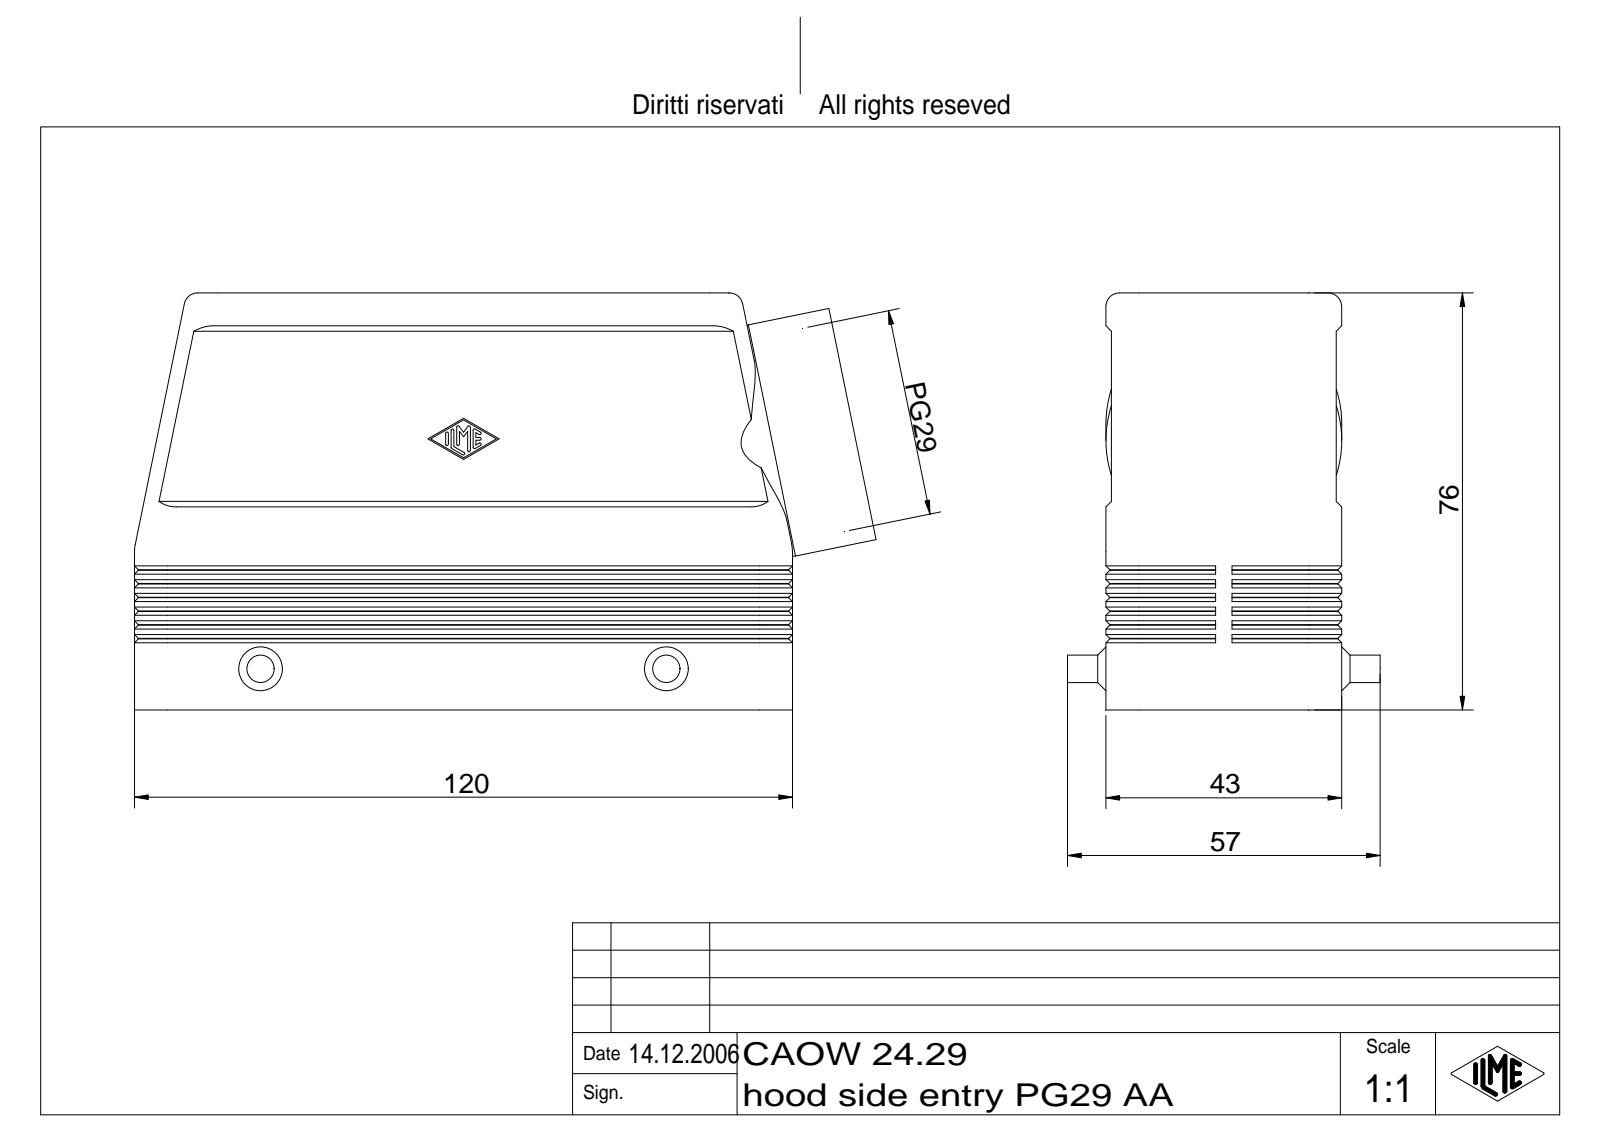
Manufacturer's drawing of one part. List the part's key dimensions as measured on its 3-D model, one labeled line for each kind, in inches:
Part name (STEP PRODUCT): CAO Tüllengehäuse 2 Bügel für einen Einsatz
STEP written by: Autodesk Inventor 7 (AUTOMOTIVE_DESIGN)
Units: inches
Bodies: 1 solid, 526 faces (192 planar, 134 cylindrical, 200 other)
Overall size (bounding box): 5.324 × 2.992 × 2.244
Volume: 5.373 in³ · Surface area: 89.25 in²
Round holes (diameter × count): ⌀1.318 ×1, ⌀1.397 ×1
Round bosses / shafts (diameter × count): ⌀0.197 ×2, ⌀1.693 ×1
Partial cylindrical surfaces — rounded edges, fillets, slot ends (radius × count): R0.01 ×14, R0.236 ×10, R0.079 ×4, R0.098 ×4, R0.118 ×4, R0.209 ×2
Main face-to-face distances: 0.118, 1.457, 1.575, 0.079, 1.535, 0.039, 1.654, 1.693, 1.614, 0.07
